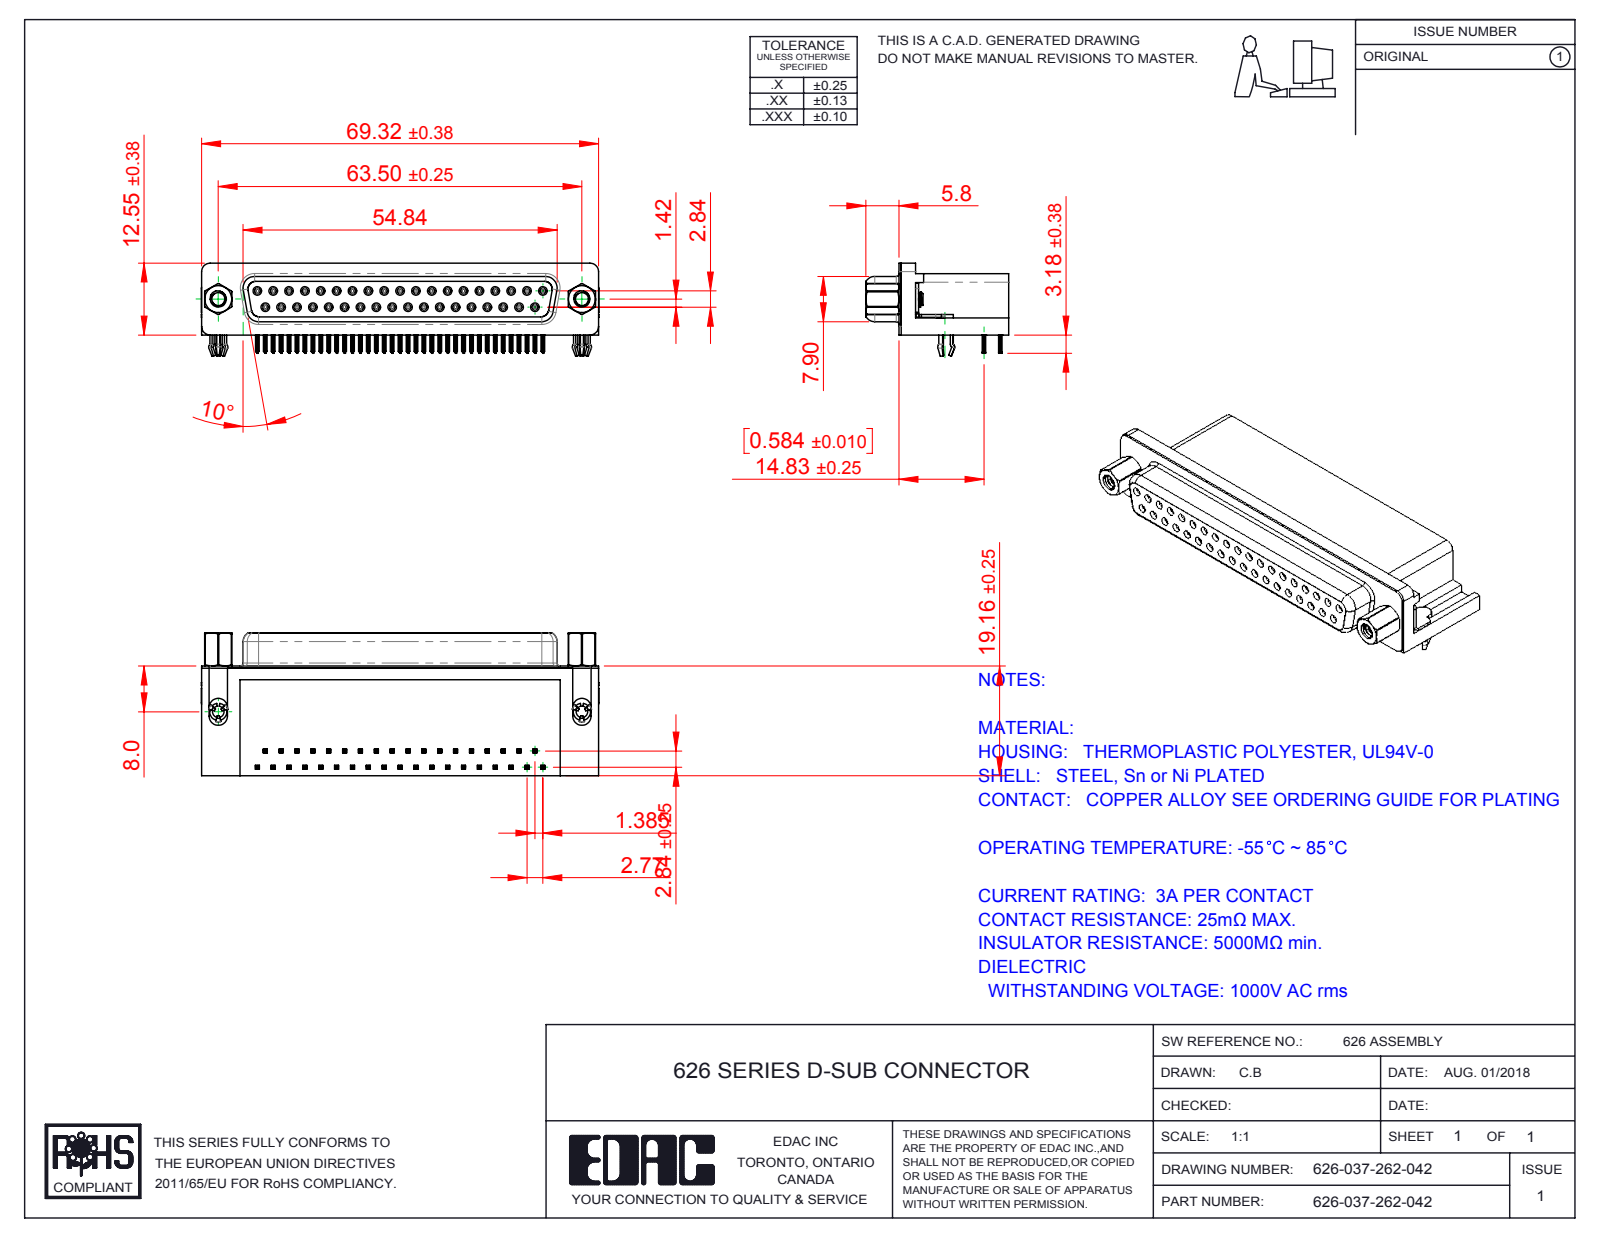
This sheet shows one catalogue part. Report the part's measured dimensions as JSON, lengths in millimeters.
{"part_name": "626 Contact Bottom; 626-037-262-042; 626 Housing_37 Socket; 626 3 Prong Board Lock (+3 more)", "step_written_by": "SolidWorks 2016 (CONFIG_CONTROL_DESIGN)", "units": "millimeters", "bodies": {"solids": 43, "faces": 5702, "planar": 2546, "cylindrical": 1338, "other": 1818}, "overall_size": [69.4, 24.96, 16.25], "volume_mm3": 14850, "surface_area_mm2": 15560, "round_holes": [[0.8, 37], [0.9, 37], [2, 2], [2.29, 2], [4, 2], [4.8, 2], [5, 2]], "round_bosses_or_shafts": [[1.2, 37], [4.9, 2], [3, 2], [2.79, 2]], "partial_cylinders_radius": [[0.1, 296], [0.15, 148], [0.35, 74], [0.34, 37], [0.28, 18], [1, 18], [1.35, 8], [1.6, 8]], "face_to_face_distances": [10.34, 0.4, 2.84, 6.2, 18.76, 0.45, 7.1, 3.17, 0.85, 7.05], "hole_center_spacings": [3.16, 2.77, 5.54, 8.31, 11.08, 22.16, 13.85, 19.39]}
